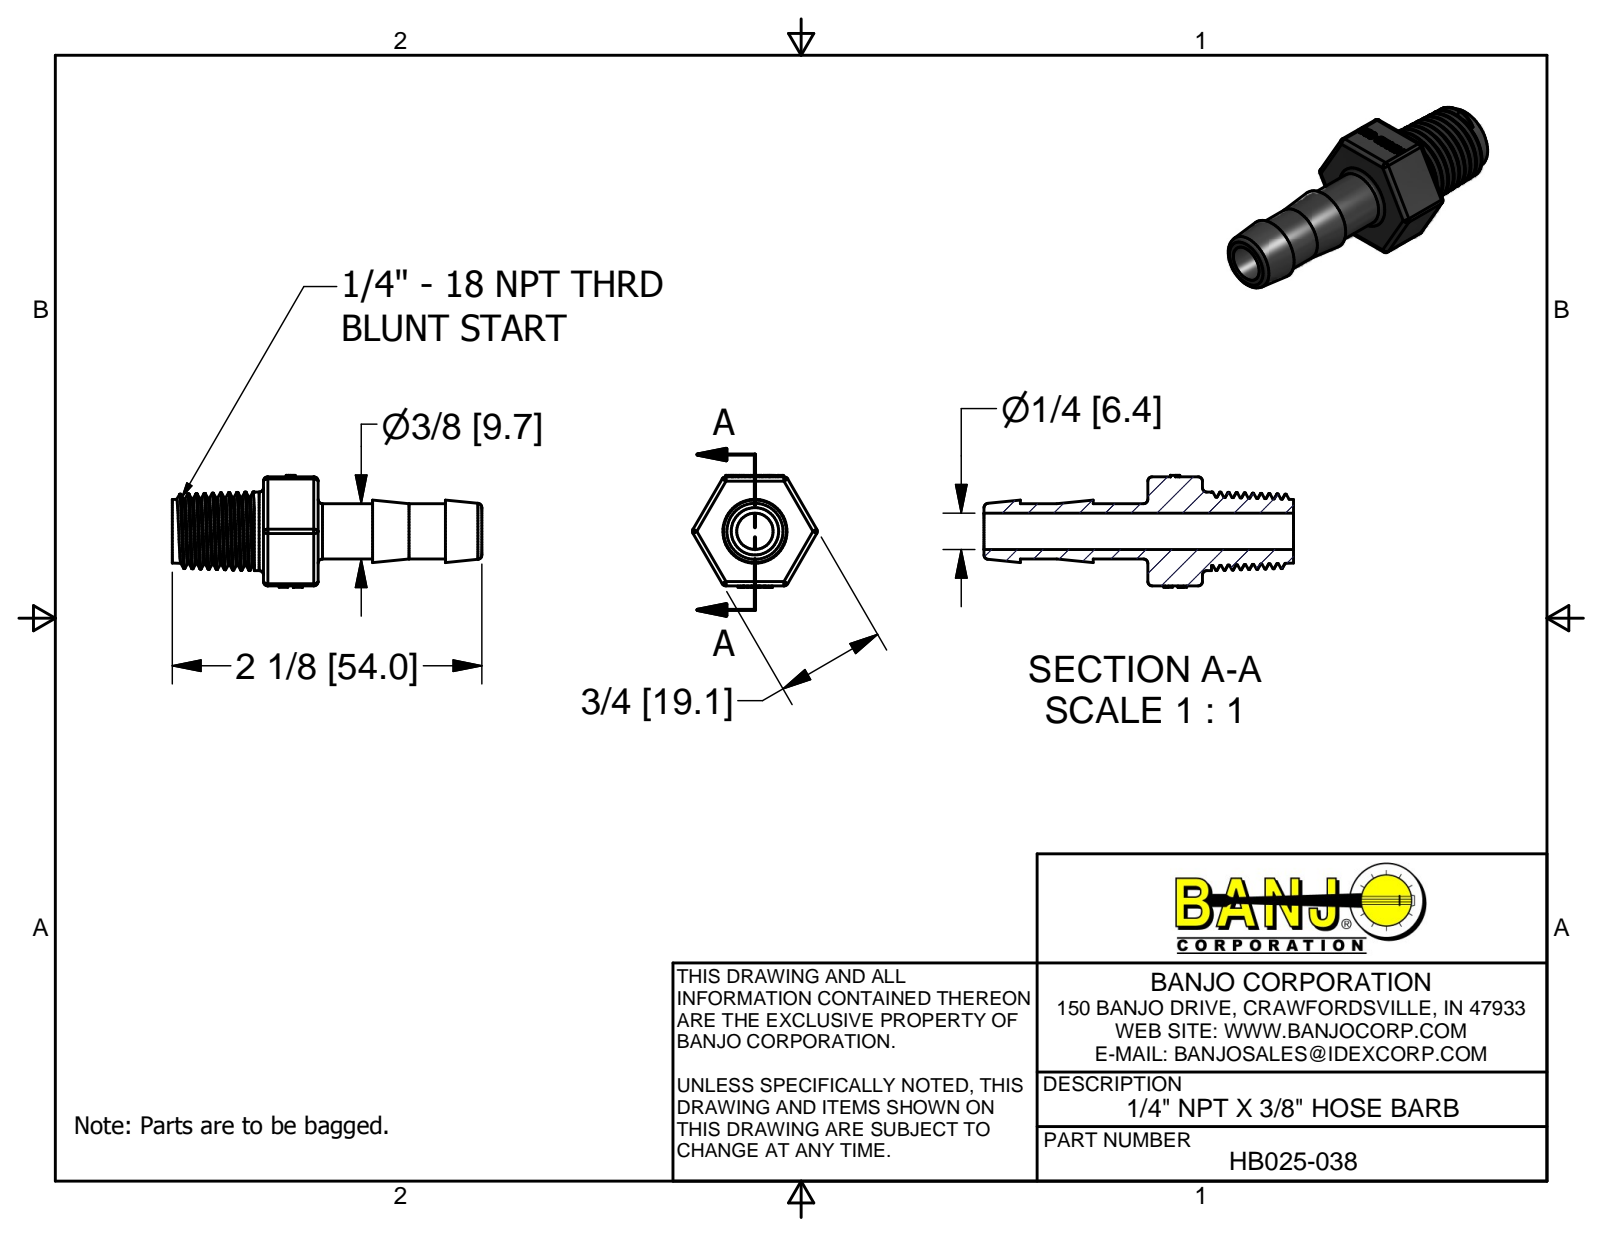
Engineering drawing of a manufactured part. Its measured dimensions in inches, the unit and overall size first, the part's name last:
Units: inches
Overall size (bounding box): 2.125 × 0.857 × 0.77
Round holes (diameter × count): ⌀0.25 ×1
Round bosses / shafts (diameter × count): ⌀0.54 ×1, ⌀0.38 ×1
Partial cylindrical surfaces — rounded edges, fillets, slot ends (radius × count): R0.03 ×18, R0.04 ×1, R0.145 ×1
Main face-to-face distances: 0.75, 0.375, 1, 0.625, 1.124, 1.5, 2.125, 0.25, 0.75, 0.5
Volume: 0.332 in³ · Surface area: 6.371 in²
Bodies: 1 solid, 350 faces (144 planar, 25 cylindrical, 181 other)
Part name (STEP PRODUCT): HB025-038
STEP written by: Autodesk Inventor 2014 (AUTOMOTIVE_DESIGN)
